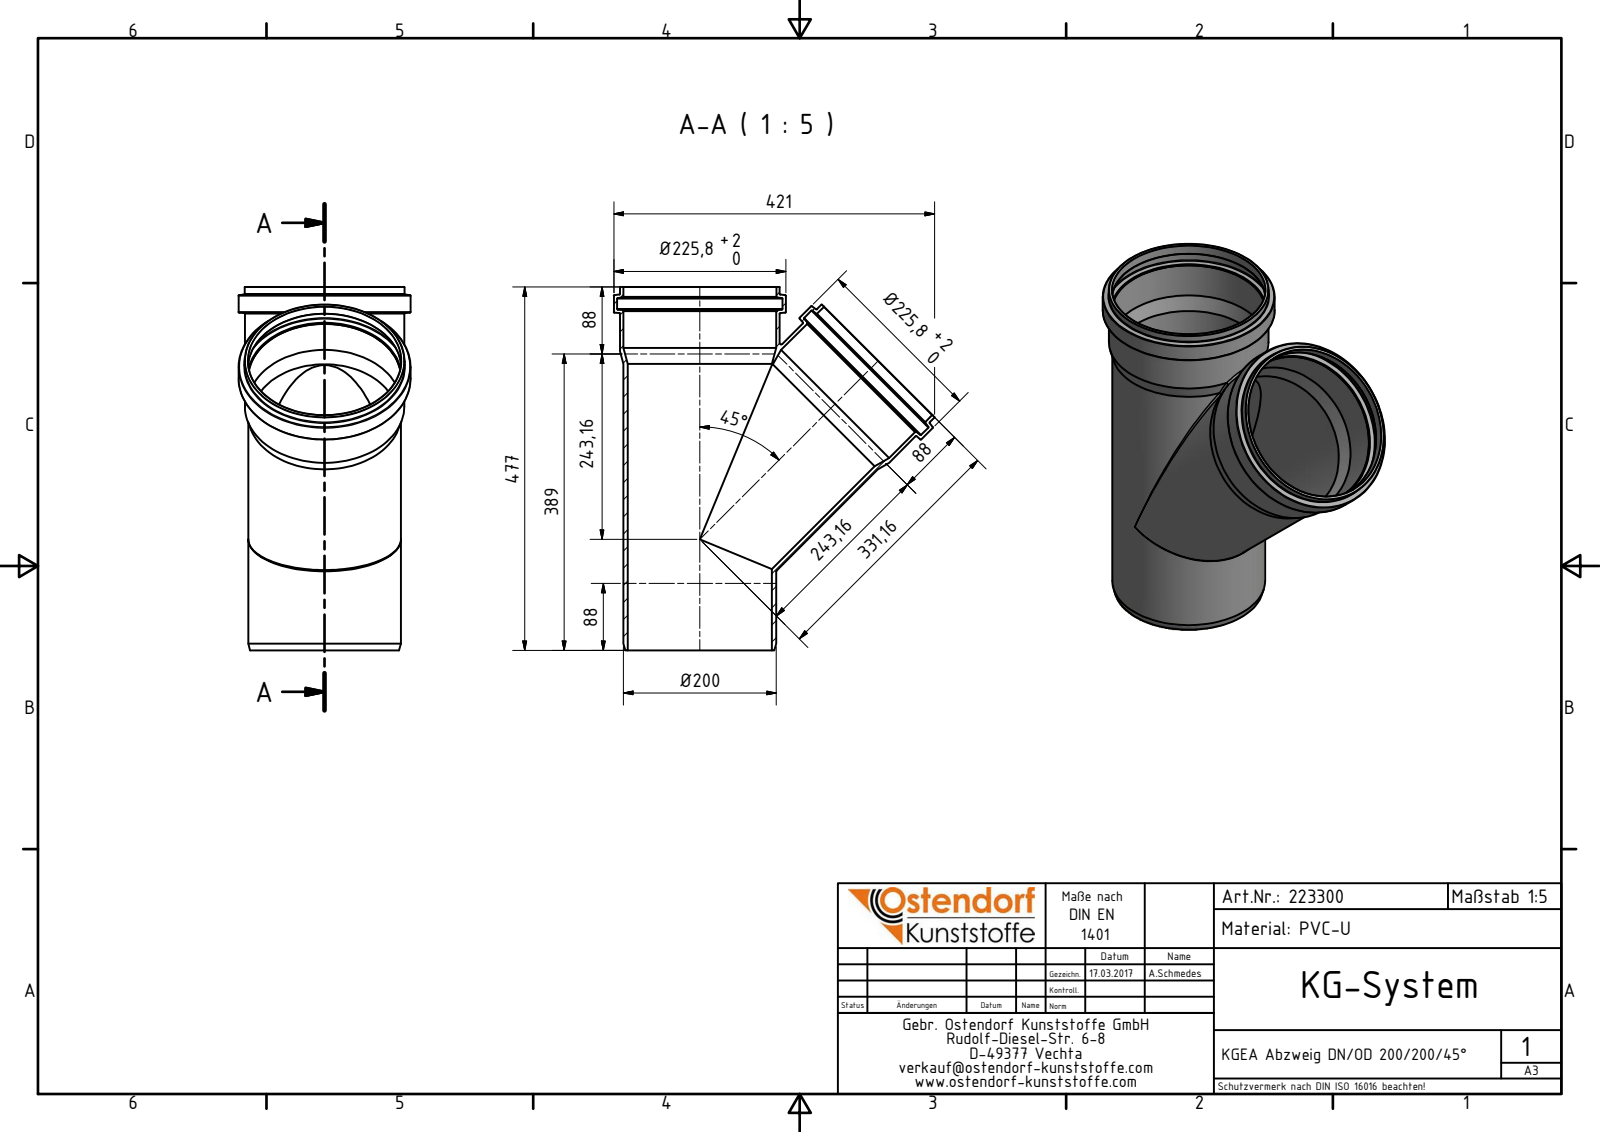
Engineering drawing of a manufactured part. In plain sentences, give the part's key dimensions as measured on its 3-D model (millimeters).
The part is named "223300 KGEA Abzweig DN_OD 200_200_45°". Its 3-D file was written by "Autodesk Inventor 2016 (AUTOMOTIVE_DESIGN)". It is 1 solid with 62 faces: 5 planar, 18 cylindrical and 39 other. Overall it measures 477 by 421 by 225.8 millimeters. Its volume is 2 161 000 cubic millimeters and its surface area 832 789 square millimeters. Round holes: 3 of diameter 200.9, 2 of diameter 189.3, 2 of diameter 200.6, 2 of diameter 217. Round bosses or shafts: 2 of diameter 225.8, 2 of diameter 209.7, 2 of diameter 209.4, 2 of diameter 200.5. The main face-to-face distances are 477, 31.77, 445.23.
